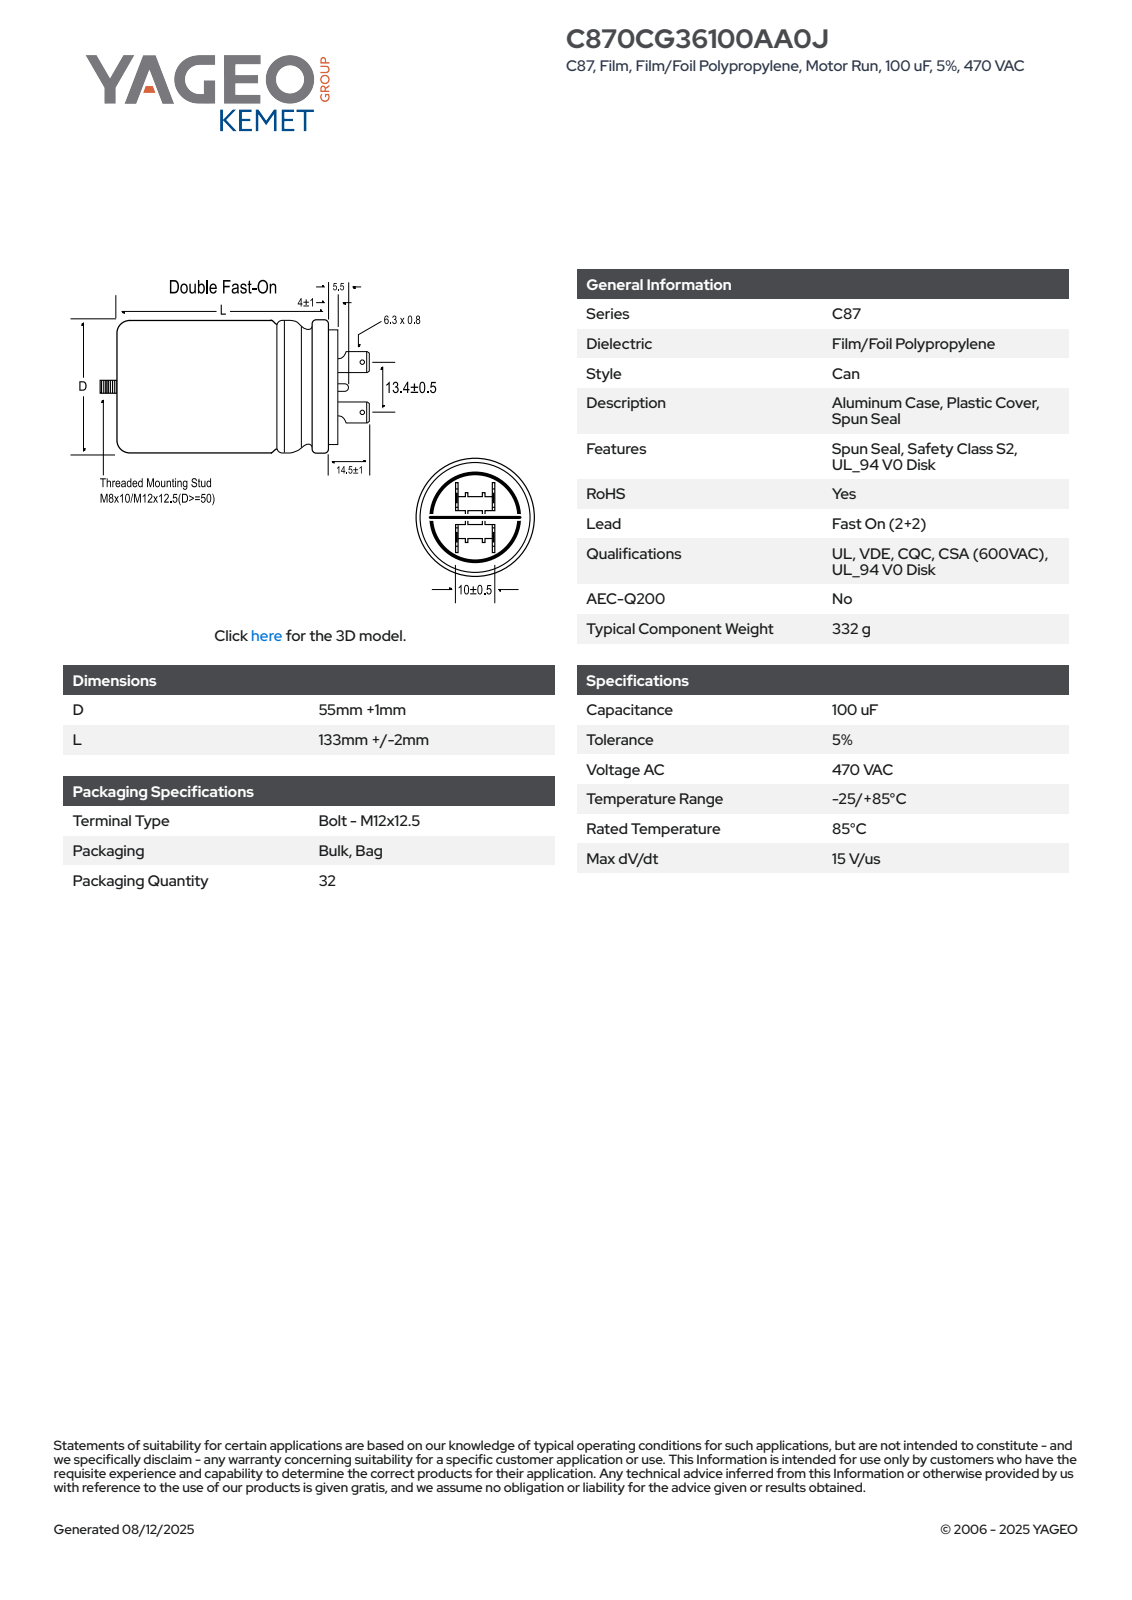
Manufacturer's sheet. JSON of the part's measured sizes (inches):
{"part_name": "CFM_C87DF_55X133_D56L135", "step_written_by": "SolidWorks 2014 (AUTOMOTIVE_DESIGN)", "units": "inches", "bodies": {"solids": 1, "faces": 153, "planar": 52, "cylindrical": 58, "other": 43}, "overall_size": [6.417, 2.205, 2.205], "volume_in3": 20.47, "surface_area_in2": 47.94, "round_holes": [[0.047, 2]], "round_bosses_or_shafts": [[2.205, 1], [1.882, 1], [0.472, 1]], "partial_cylinders_radius": [[0.01, 9], [0.157, 2], [1.102, 1]], "face_to_face_distances": [5.512, 4.98, 0.531, 5.315, 0.335, 0.197, 0.031, 0.382, 4.246, 0.734], "hole_center_spacings": [0.547]}
